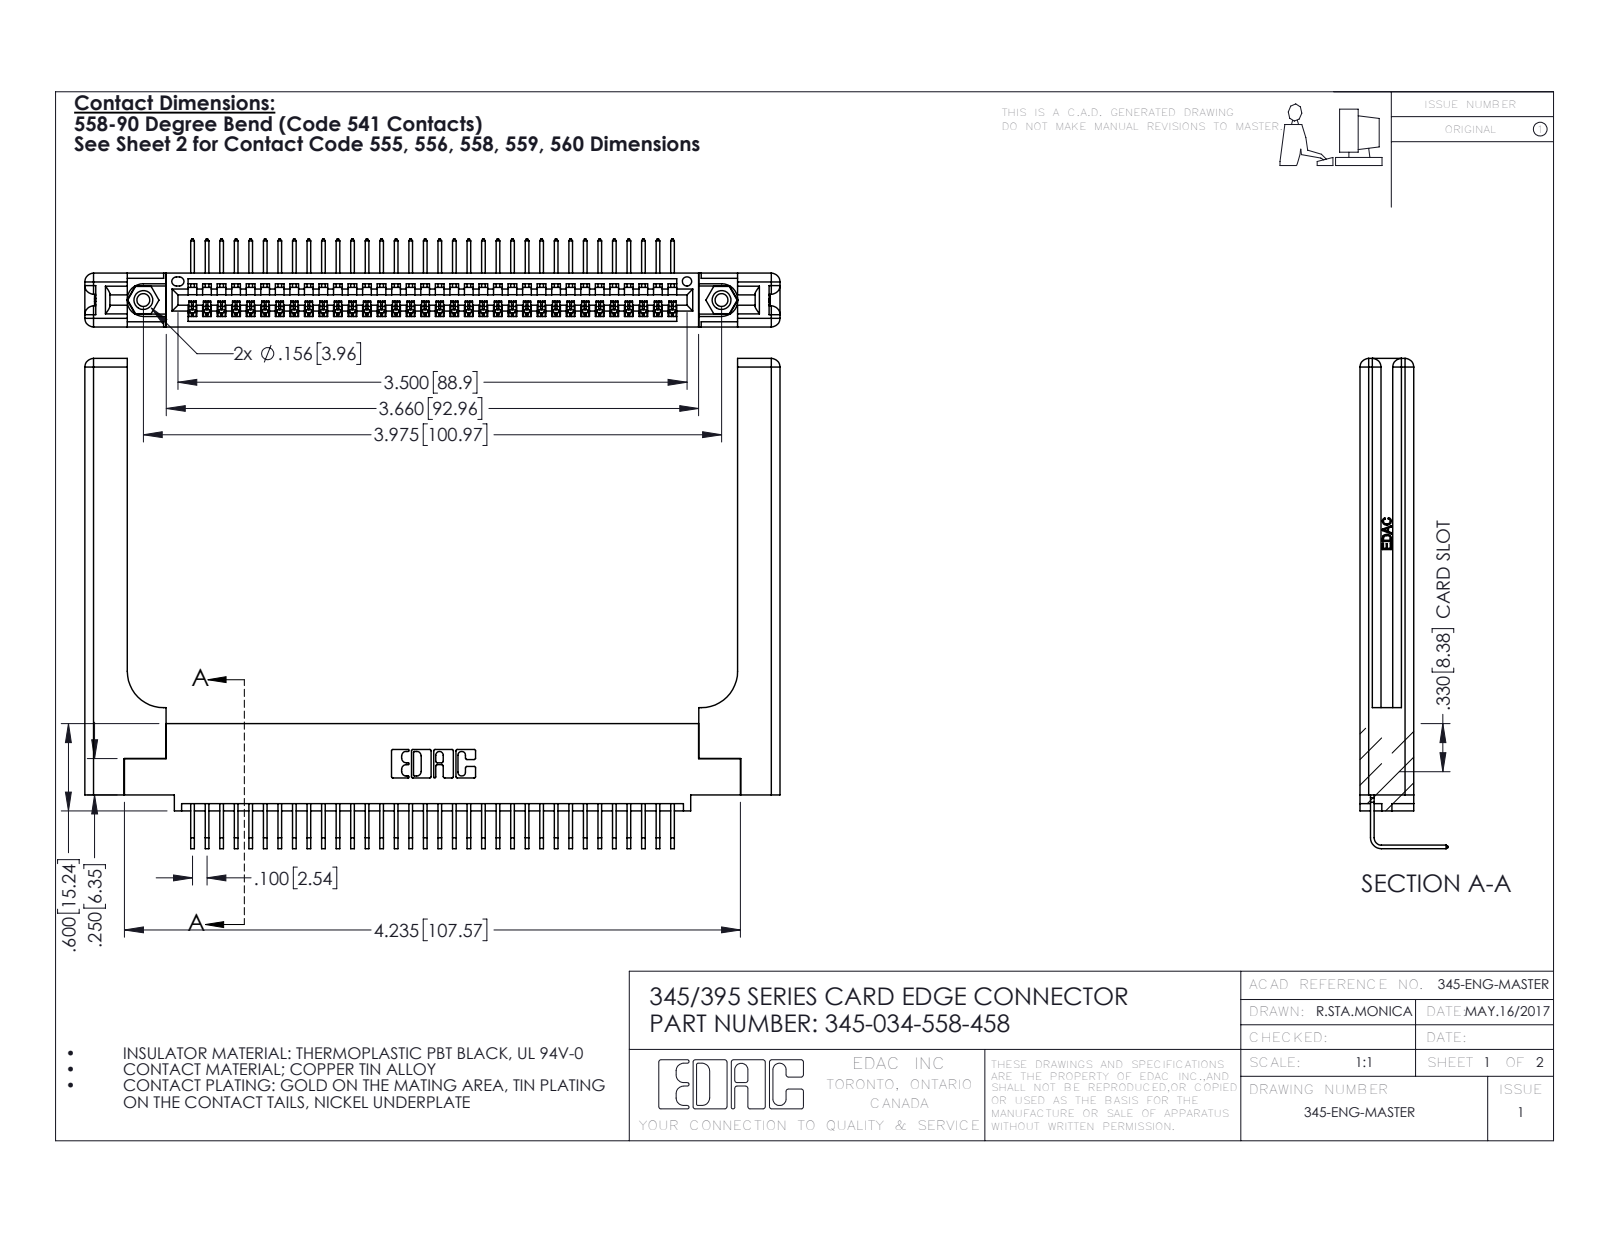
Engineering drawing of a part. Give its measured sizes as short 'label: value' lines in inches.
name: 345-292-001_558 Tail - 2; 345-250-001_345-250-001-102; 345 Part_0.110 Offset - 0.156 Dia-TH; 345-220-058_345-220-058 (+1 more)
written by: SolidWorks 2016 (CONFIG_CONTROL_DESIGN)
unit: in
bodies: 39 solids, 2426 faces (1660 planar, 706 cylindrical, 60 other)
size: 4.779 × 3.369 × 0.605
volume: 1.221 in³; area: 32.91 in²
holes: 2× ⌀0.089, 2× ⌀0.125, 2× ⌀0.156, 1× ⌀0.064
bosses: 2× ⌀0.155
rounds: 68× R0.006, 22× R0.01, 16× R0.06, 6× R0.007, 6× R0.031, 3× R0.026, 2× R0.03, 2× R0.031
face distances: 0.37, 0.072, 0.298, 0.2, 0.098, 0.272, 0.025, 0.148, 0.15, 0.077
hole spacings: 0.27, 3.74, 3.975
